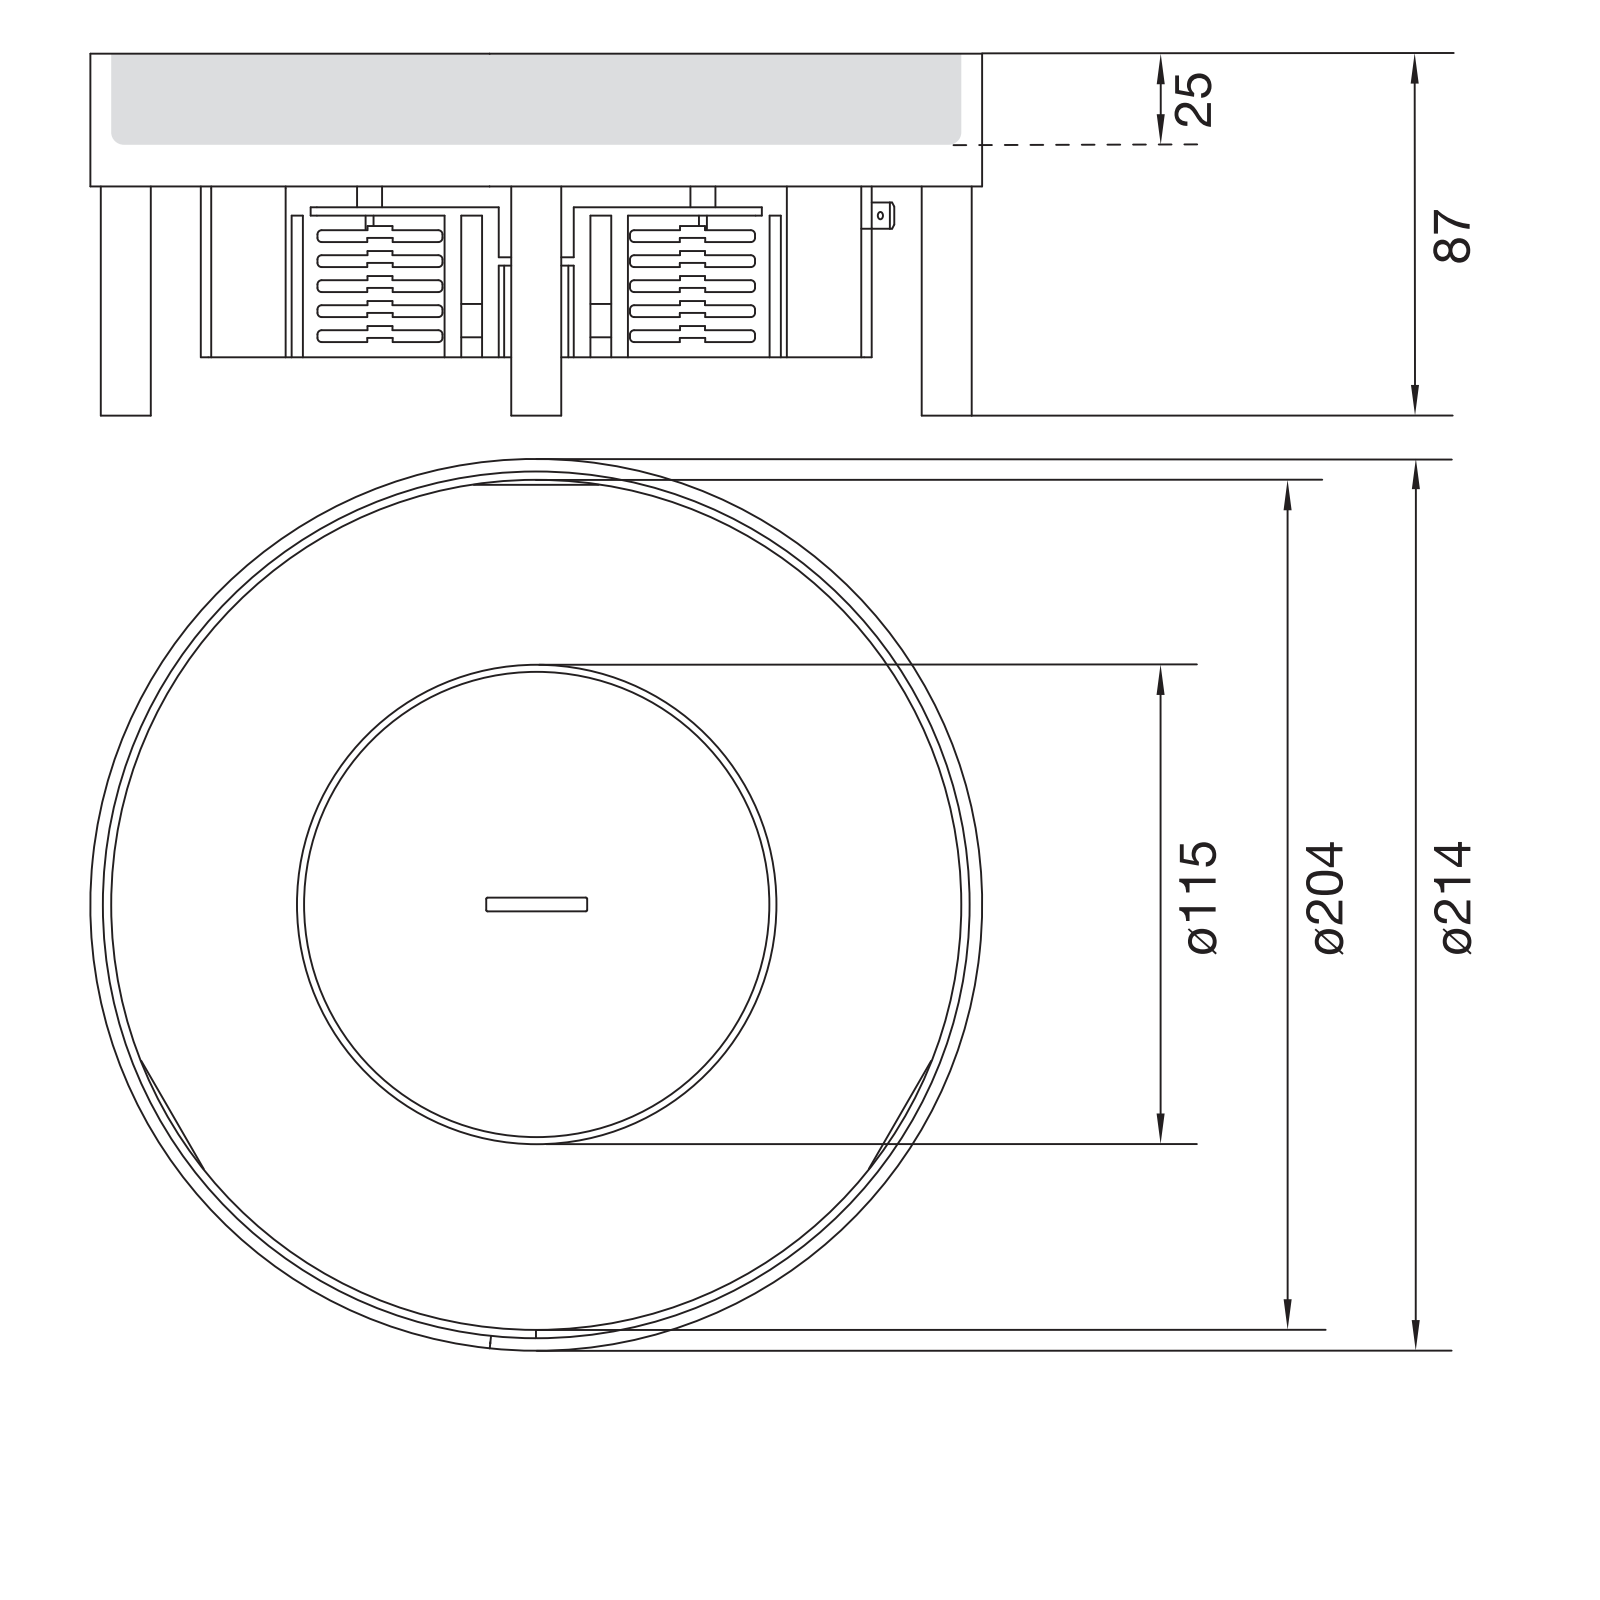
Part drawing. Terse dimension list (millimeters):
name: T-00671; T-00672; T-00673; T-00675 (+8 more)
written by: CREO PARAMETRIC BY PTC INC, 2022024 (AUTOMOTIVE_DESIGN)
unit: mm
bodies: 16 solids, 240 faces (113 planar, 117 cylindrical, 10 other)
size: 214 × 214 × 87
volume: 303 360 mm³; area: 293 255 mm²
holes: 6× ⌀3.8, 4× ⌀6.8, 4× ⌀8.5, 4× ⌀10.1, 3× ⌀4.5, 1× ⌀80.59, 1× ⌀90, 1× ⌀101, 1× ⌀107, 1× ⌀108.6, 1× ⌀111.4, 1× ⌀112
bosses: 4× ⌀12, 4× ⌀9.85, 1× ⌀214, 1× ⌀208, 1× ⌀204, 1× ⌀115, 1× ⌀111.6, 1× ⌀111
rounds: 8× R0.5, 3× R5, 1× R43
face distances: 2, 2.5, 5, 25, 27, 7, 153.5, 32, 3, 30
hole spacings: 41.16, 97.39, 98.5, 106.34, 139.3, 164.52, 191.52, 54
